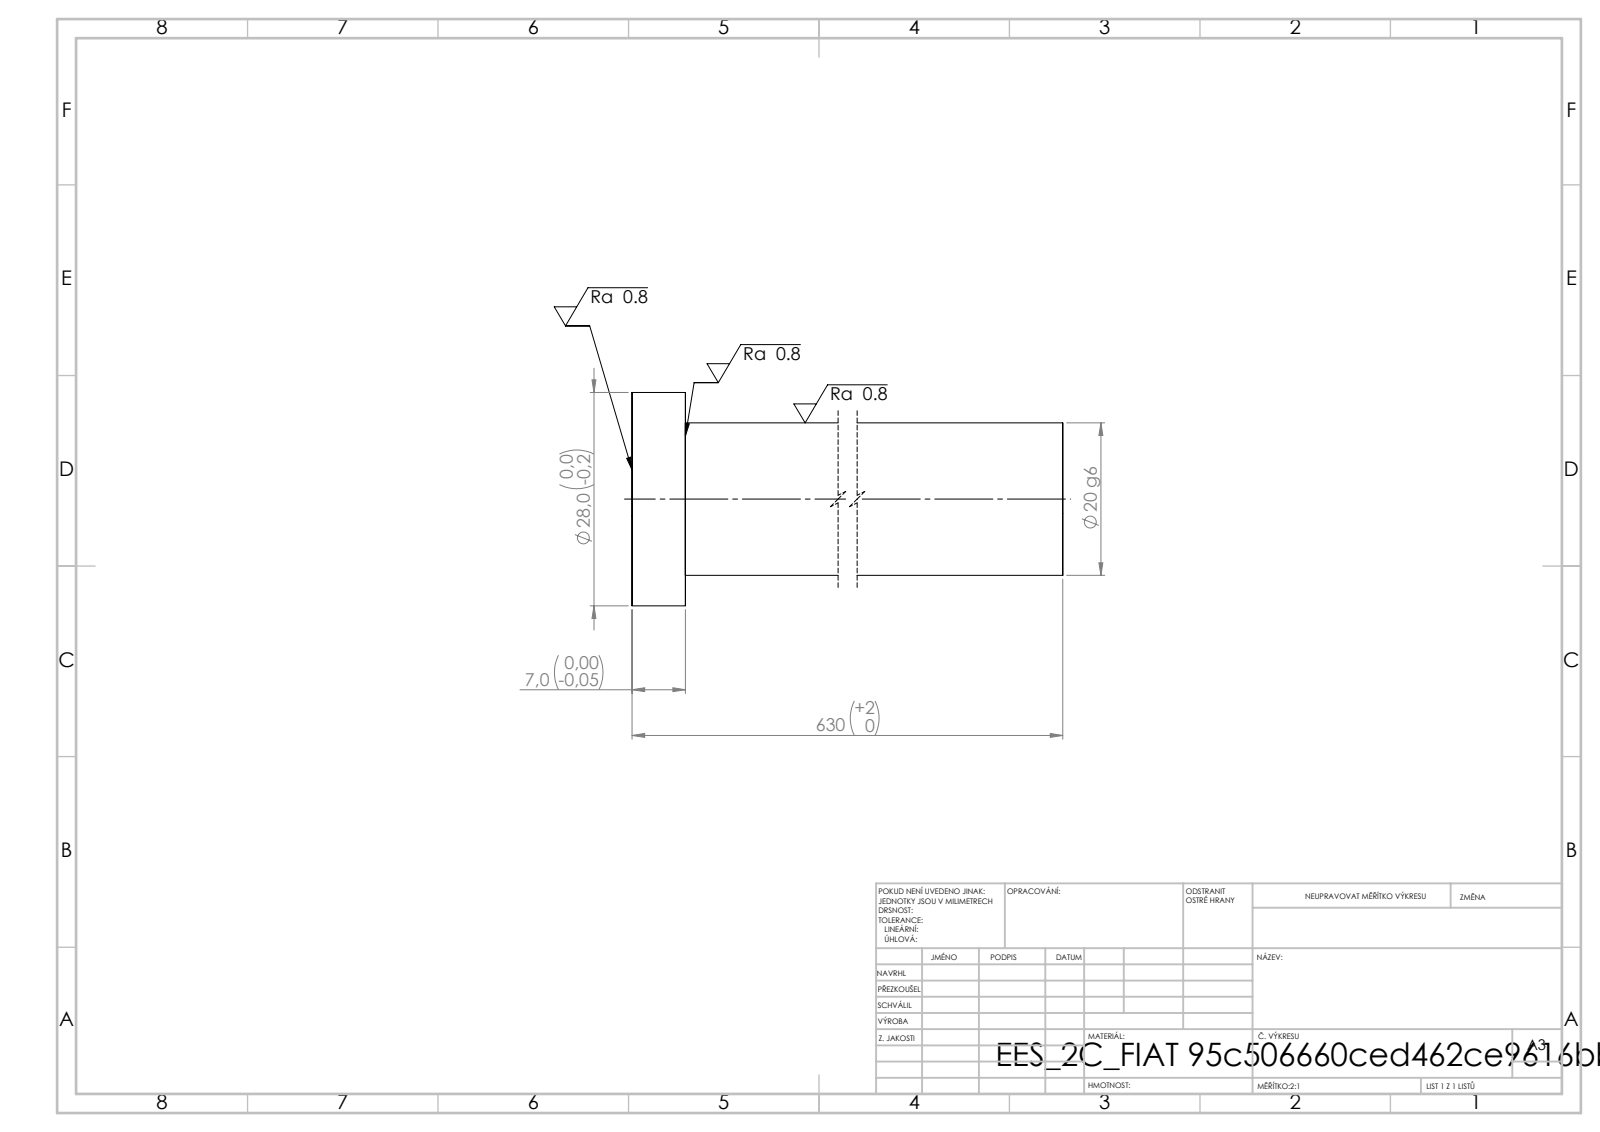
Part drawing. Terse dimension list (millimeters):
written by: SolidWorks 2019 (CONFIG_CONTROL_DESIGN)
unit: mm
bodies: 1 solid, 7 faces (3 planar, 4 cylindrical, 0 other)
size: 630 × 28 × 28
volume: 200 031 mm³; area: 40 992 mm²
bosses: 1× ⌀28, 1× ⌀20
face distances: 630, 7, 623
